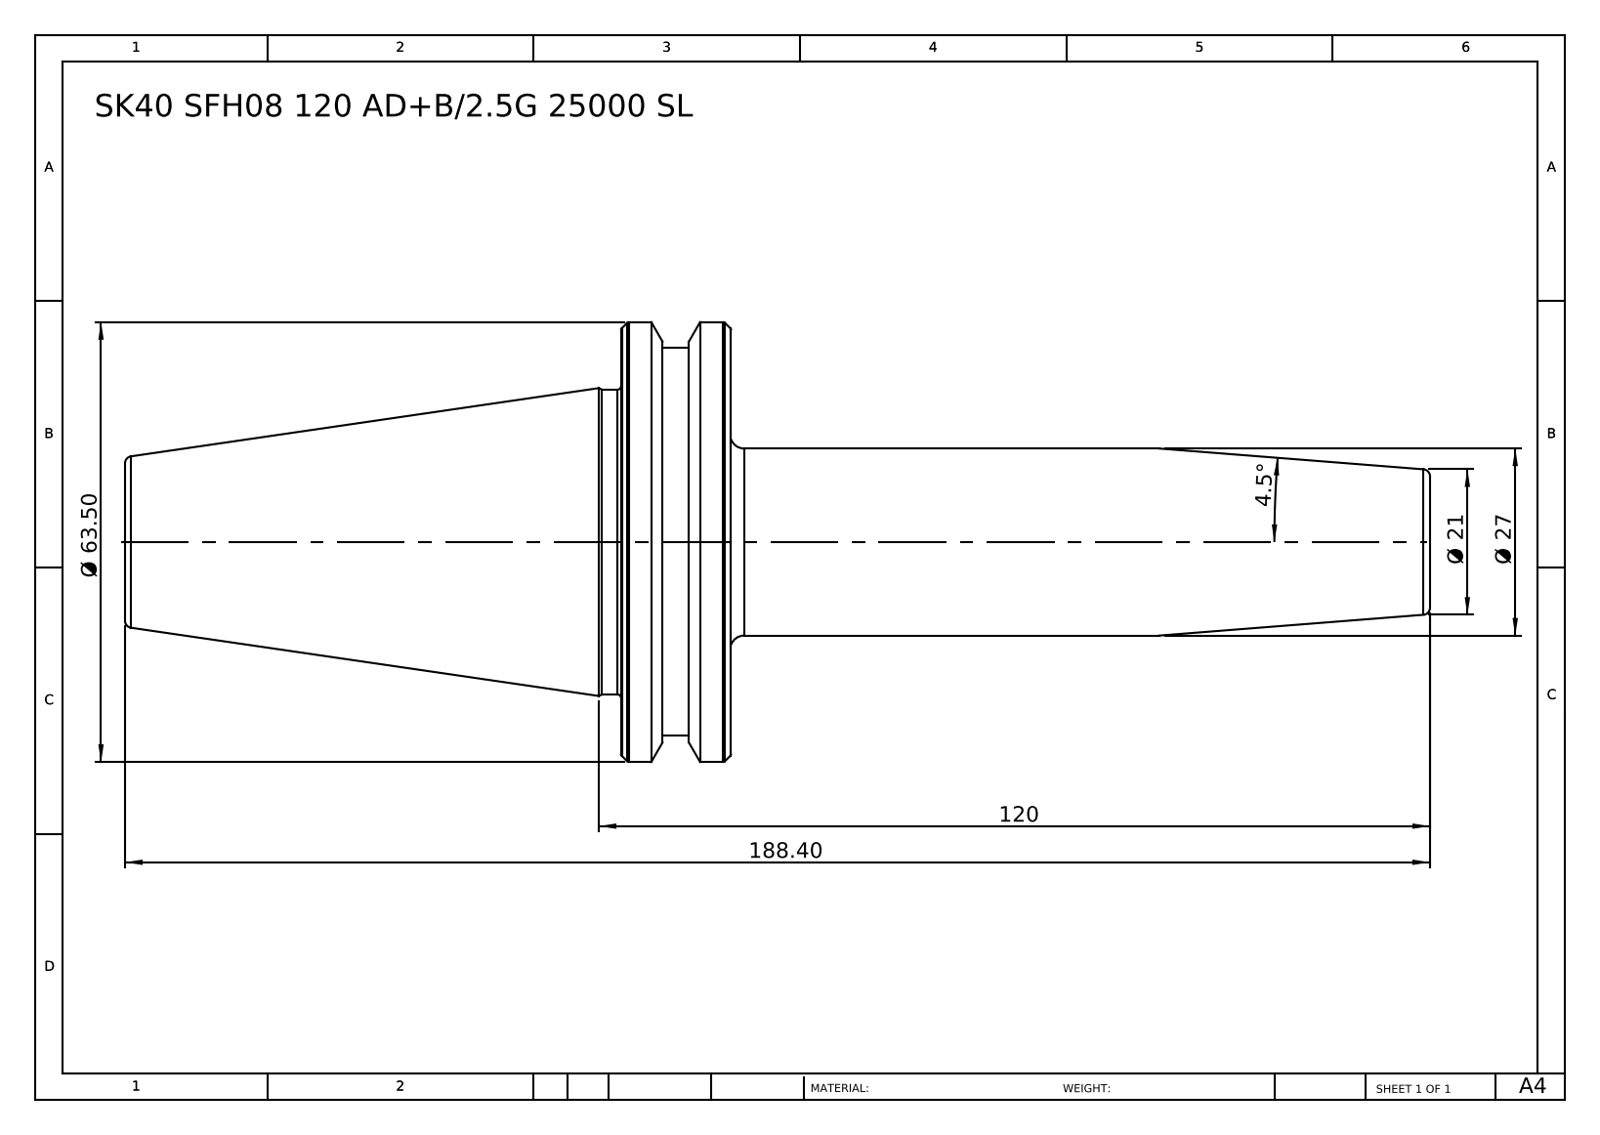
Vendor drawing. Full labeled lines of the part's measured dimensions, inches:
Part name (STEP PRODUCT): SK40 SFH08 120 AD+B-2.5G 25000 SL
STEP written by: SolidWorks 2014 (CONFIG_CONTROL_DESIGN)
Units: inches
Bodies: 1 solid, 46 faces (6 planar, 10 cylindrical, 30 other)
Overall size (bounding box): 7.417 × 2.5 × 2.5
Volume: 10.39 in³ · Surface area: 38.44 in²
Round bosses / shafts (diameter × count): ⌀2.5 ×1, ⌀2.205 ×1, ⌀1.732 ×1, ⌀1.063 ×1
Main face-to-face distances: 0.626, 3.445, 2.819, 3.972, 4.598, 7.417, 4.213, 0.24, 0.386, 3.205
